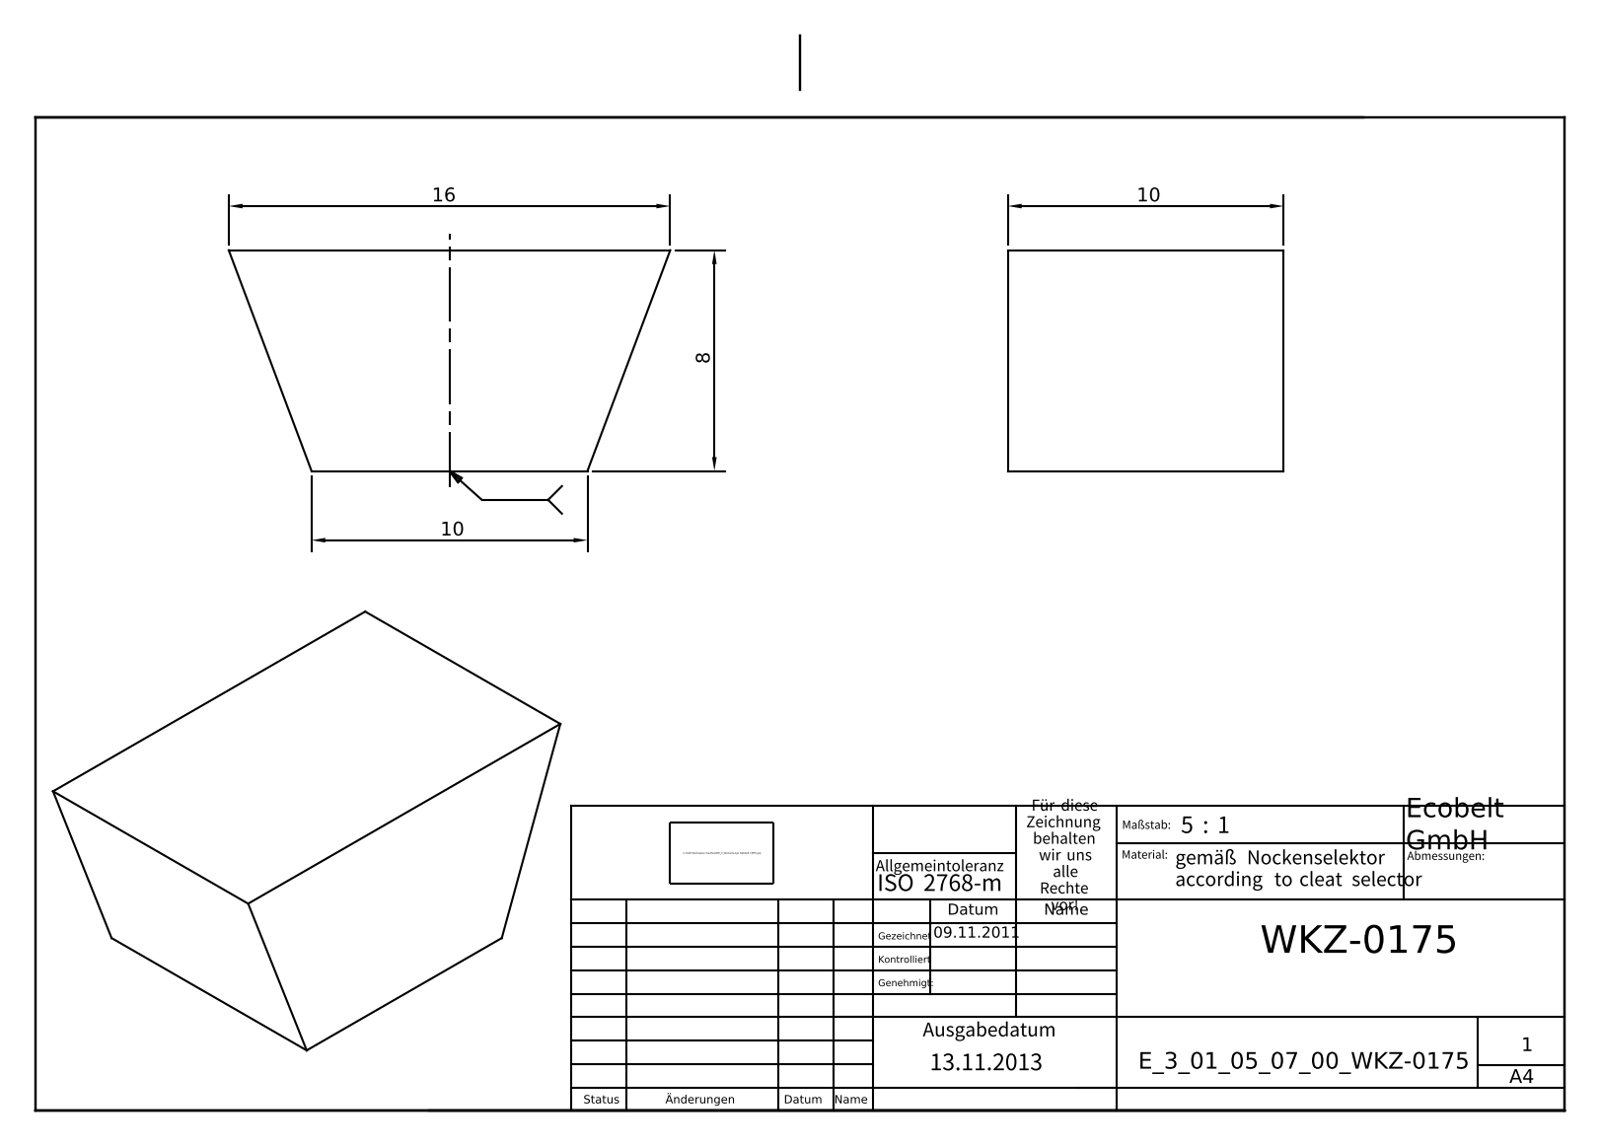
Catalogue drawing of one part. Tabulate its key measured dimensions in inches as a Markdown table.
| quantity | value |
| --- | --- |
| part name | E_3_01_05_07_00_WKZ-0175 |
| STEP written by | Autodesk Inventor 2025 (AUTOMOTIVE_DESIGN) |
| units | inches |
| bodies | 1 solid, 6 faces (6 planar, 0 cylindrical, 0 other) |
| overall size | 0.63 × 0.394 × 0.315 |
| volume | 0.063 in³ |
| surface area | 0.99 in² |
| main face-to-face distances | 0.394, 0.315 |
